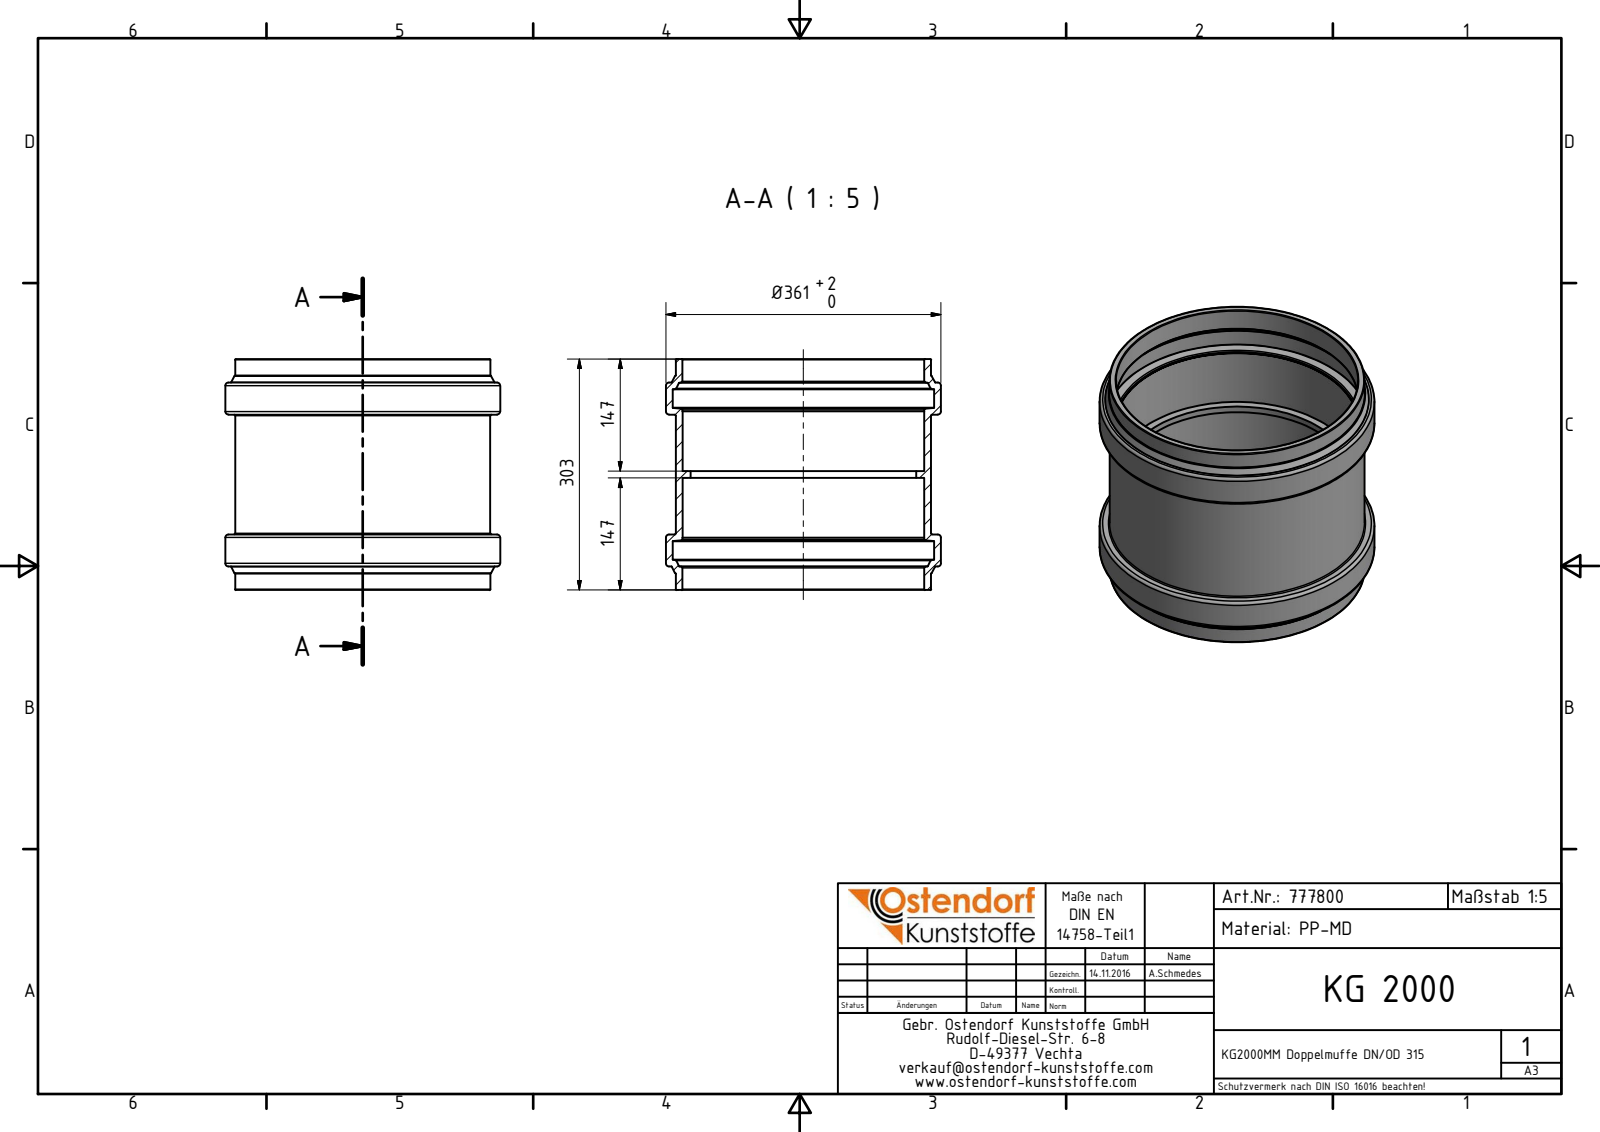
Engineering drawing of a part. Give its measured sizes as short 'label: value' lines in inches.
name: 777800 KG2000MM Doppelmuffe DN_OD 315
written by: Autodesk Inventor 2016 (AUTOMOTIVE_DESIGN)
unit: in
bodies: 1 solid, 62 faces (10 planar, 14 cylindrical, 38 other)
size: 14.205 × 14.205 × 11.929
volume: 198.9 in³; area: 1 159 in²
holes: 1× ⌀11.654, 1× ⌀12.484, 1× ⌀12.5, 1× ⌀13.512
bosses: 1× ⌀14.205, 1× ⌀13.193, 1× ⌀13.177
face distances: 2.917, 3.272, 2.87, 5.787, 6.142, 9.059, 0.354, 6.189, 11.929, 1.217
